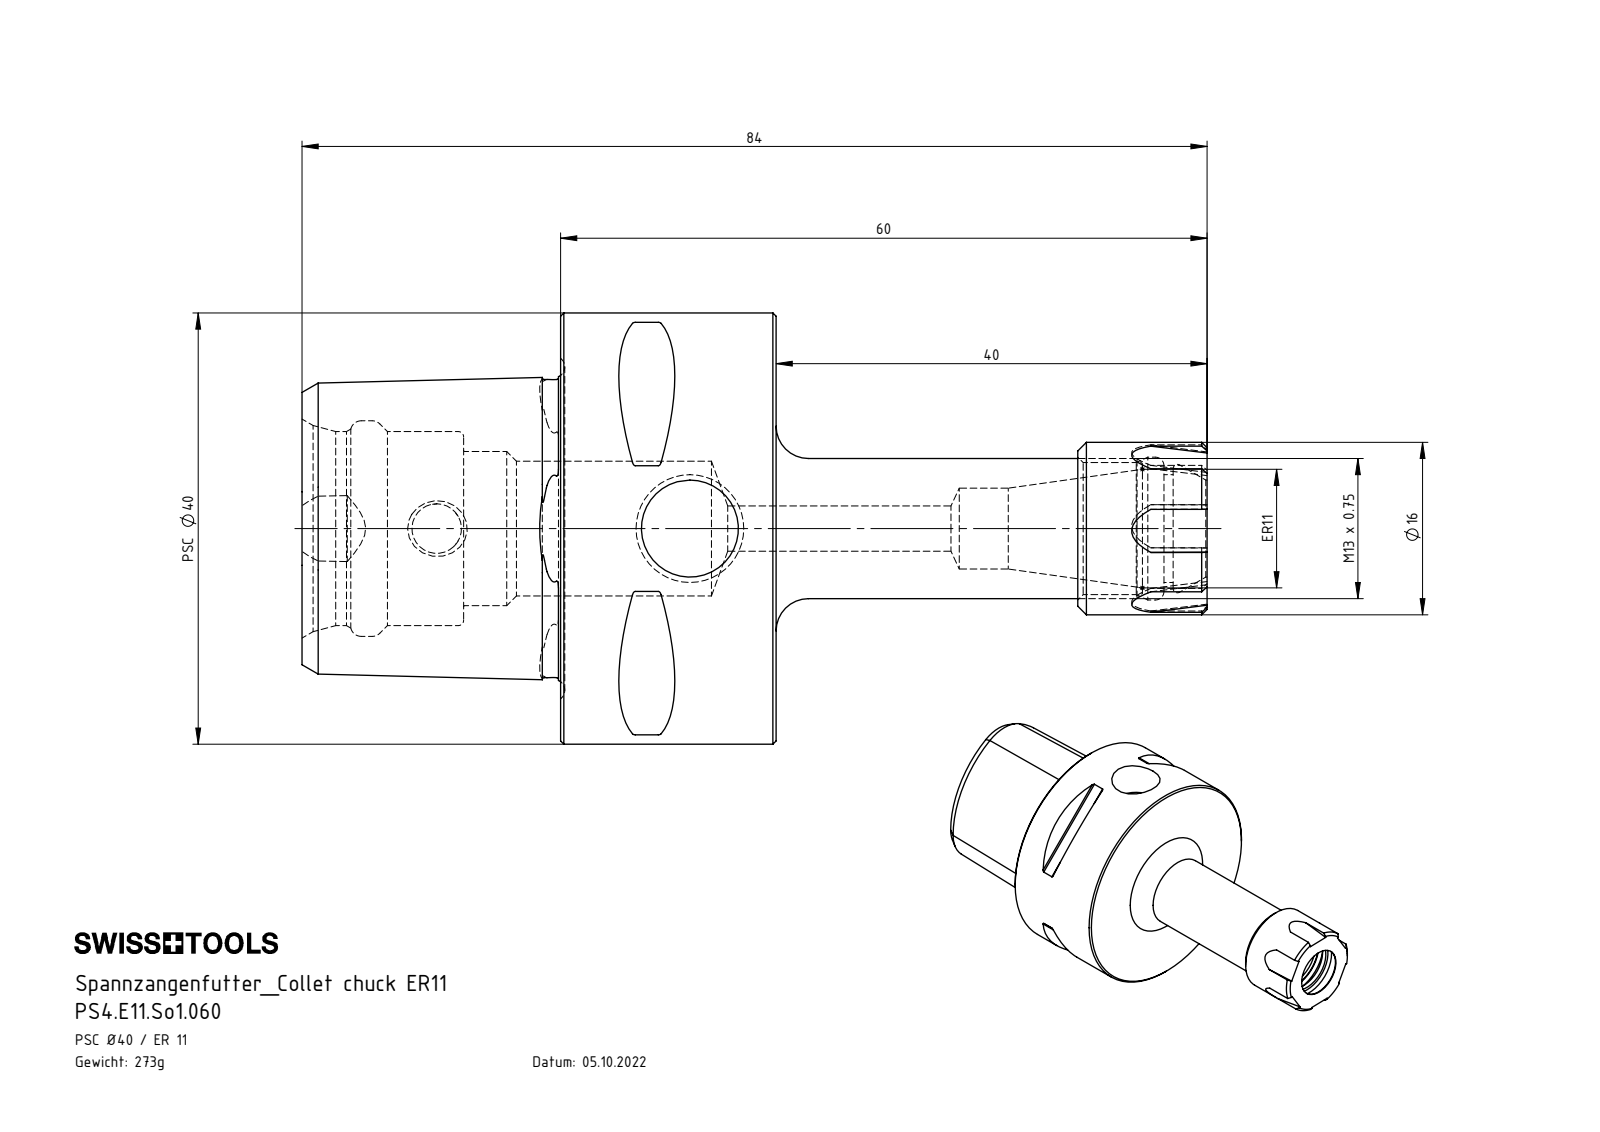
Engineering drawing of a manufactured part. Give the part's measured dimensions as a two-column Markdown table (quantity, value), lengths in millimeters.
| quantity | value |
| --- | --- |
| part name | PS4.E11.So1.060; PS4-E11.So1.060_A_Fertigbearbeitung; E11-ER1.001.012 |
| STEP written by | SolidWorks 2022 (CONFIG_CONTROL_DESIGN) |
| units | millimeters |
| bodies | 2 solids, 203 faces (43 planar, 45 cylindrical, 115 other) |
| overall size | 84 × 40 × 40 |
| volume | 34 718 mm³ |
| surface area | 12 579 mm² |
| round holes (diameter × count) | 9 × 2, 10 × 2, 4.2 × 1, 4.6 × 1, 7.5 × 1, 12.25 × 1, 12.5 × 1, 13.25 × 1, 14.3 × 1, 18 × 1, 20 × 1 |
| round bosses / shafts (diameter × count) | 40 × 1, 16 × 1, 13 × 1 |
| partial cylindrical surfaces (radius × count) | 0.3 × 8, 4 × 1 |
| main face-to-face distances | 20, 24, 44, 15.52, 84, 60, 40, 35.3, 15, 9 |
| hole center spacings | 23.5 |
